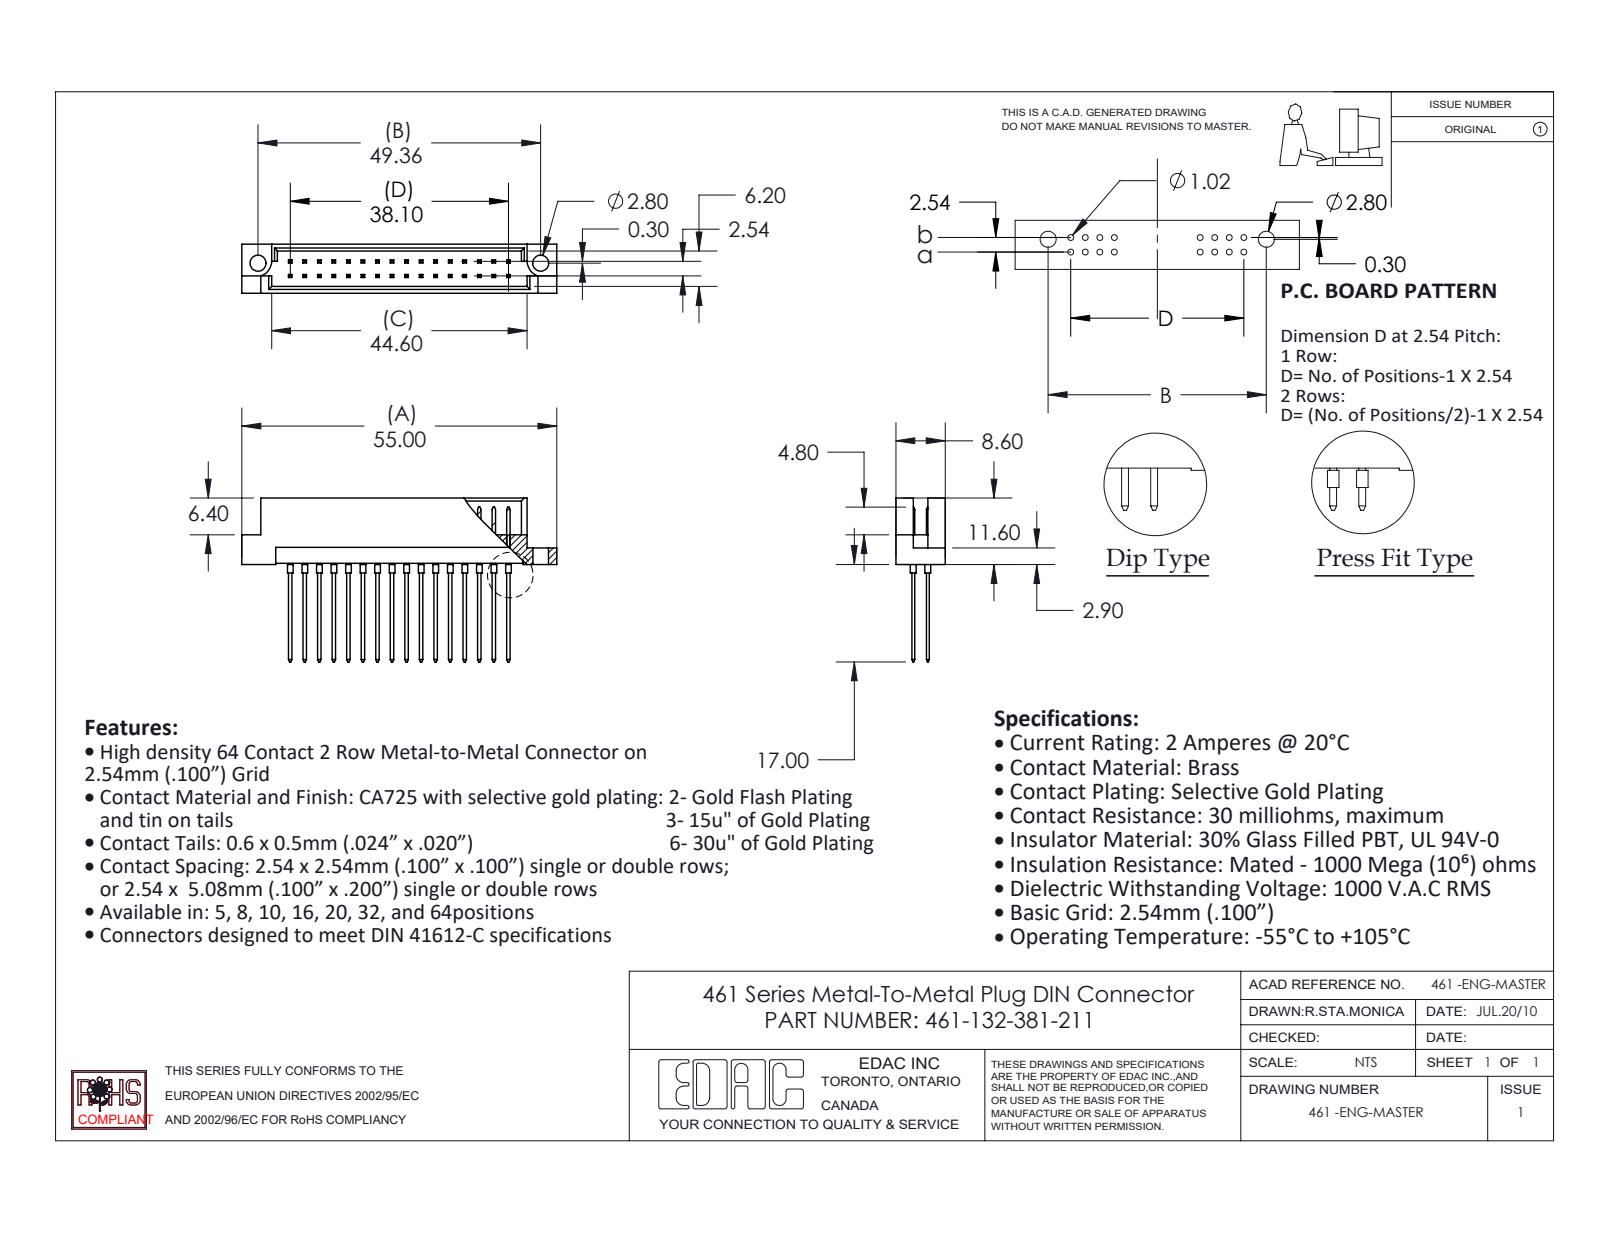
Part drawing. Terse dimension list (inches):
name: 461-290_81; 461 Part_32; 461-132-381-211
written by: SolidWorks 2020 (CONFIG_CONTROL_DESIGN)
unit: in
bodies: 33 solids, 880 faces (810 planar, 70 cylindrical, 0 other)
size: 2.165 × 1.126 × 0.339
volume: 0.179 in³; area: 8.079 in²
holes: 2× ⌀0.11
bosses: 32× ⌀0.039
rounds: 2× R0.11
face distances: 0.1, 0.047, 0.291, 0.109, 0.229, 0.062, 0.182, 0.129, 0.209, 0.082
hole spacings: 1.943
